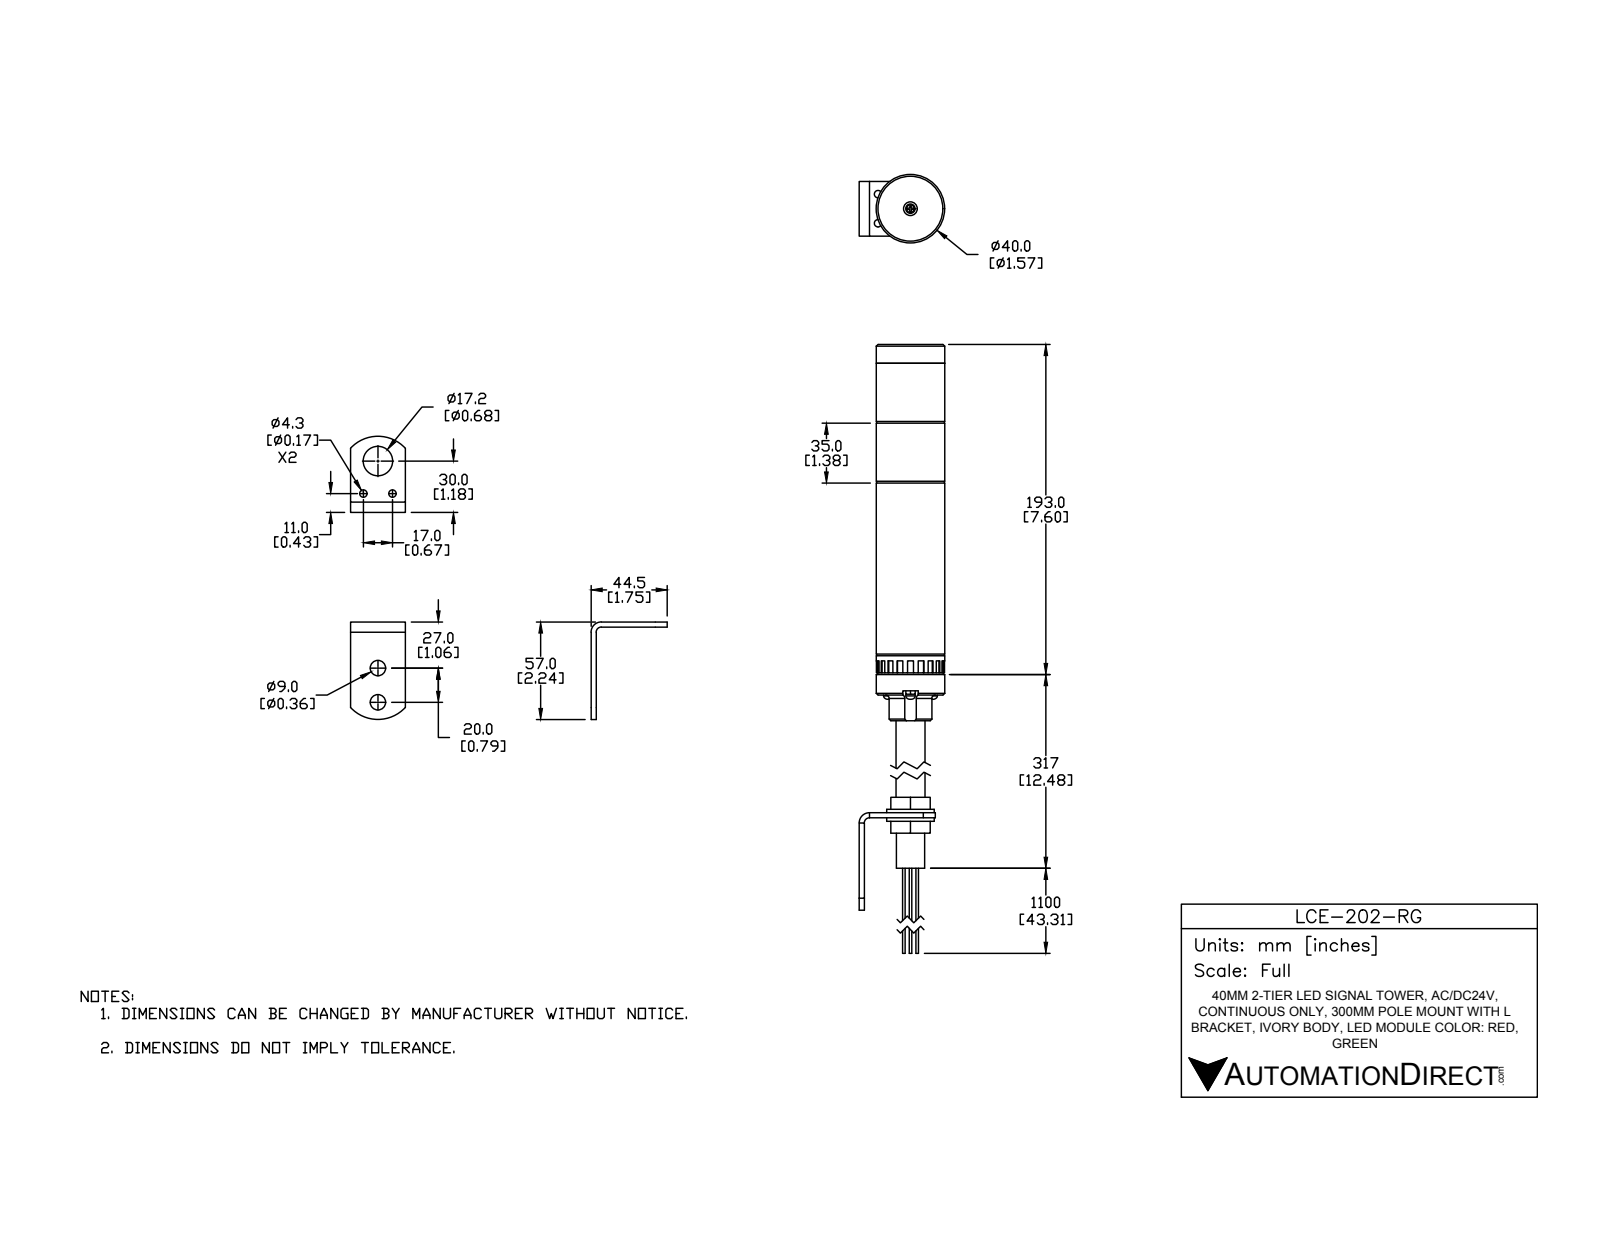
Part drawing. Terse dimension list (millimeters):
name: LCE-202-RG
written by: SolidWorks 2016 (AUTOMOTIVE_DESIGN)
unit: mm
bodies: 29 solids, 361 faces (233 planar, 108 cylindrical, 20 other)
size: 593 × 50 × 40
volume: 307 506 mm³; area: 105 236 mm²
holes: 3× ⌀3.5, 3× ⌀4, 2× ⌀4.3, 2× ⌀9.04, 1× ⌀8, 1× ⌀12, 1× ⌀17.2, 1× ⌀17.5, 1× ⌀18
bosses: 6× ⌀1.5, 4× ⌀5.5, 3× ⌀3, 1× ⌀40, 1× ⌀39.5, 1× ⌀38.5, 1× ⌀27.8, 1× ⌀17
rounds: 3× R4.5, 2× R21.79, 1× R3, 1× R6, 1× R12.5
face distances: 1, 35, 11, 34, 101, 136, 112, 147, 181, 182
hole spacings: 15, 25.98, 20.81, 6.09, 17, 17.09, 20, 20.08
